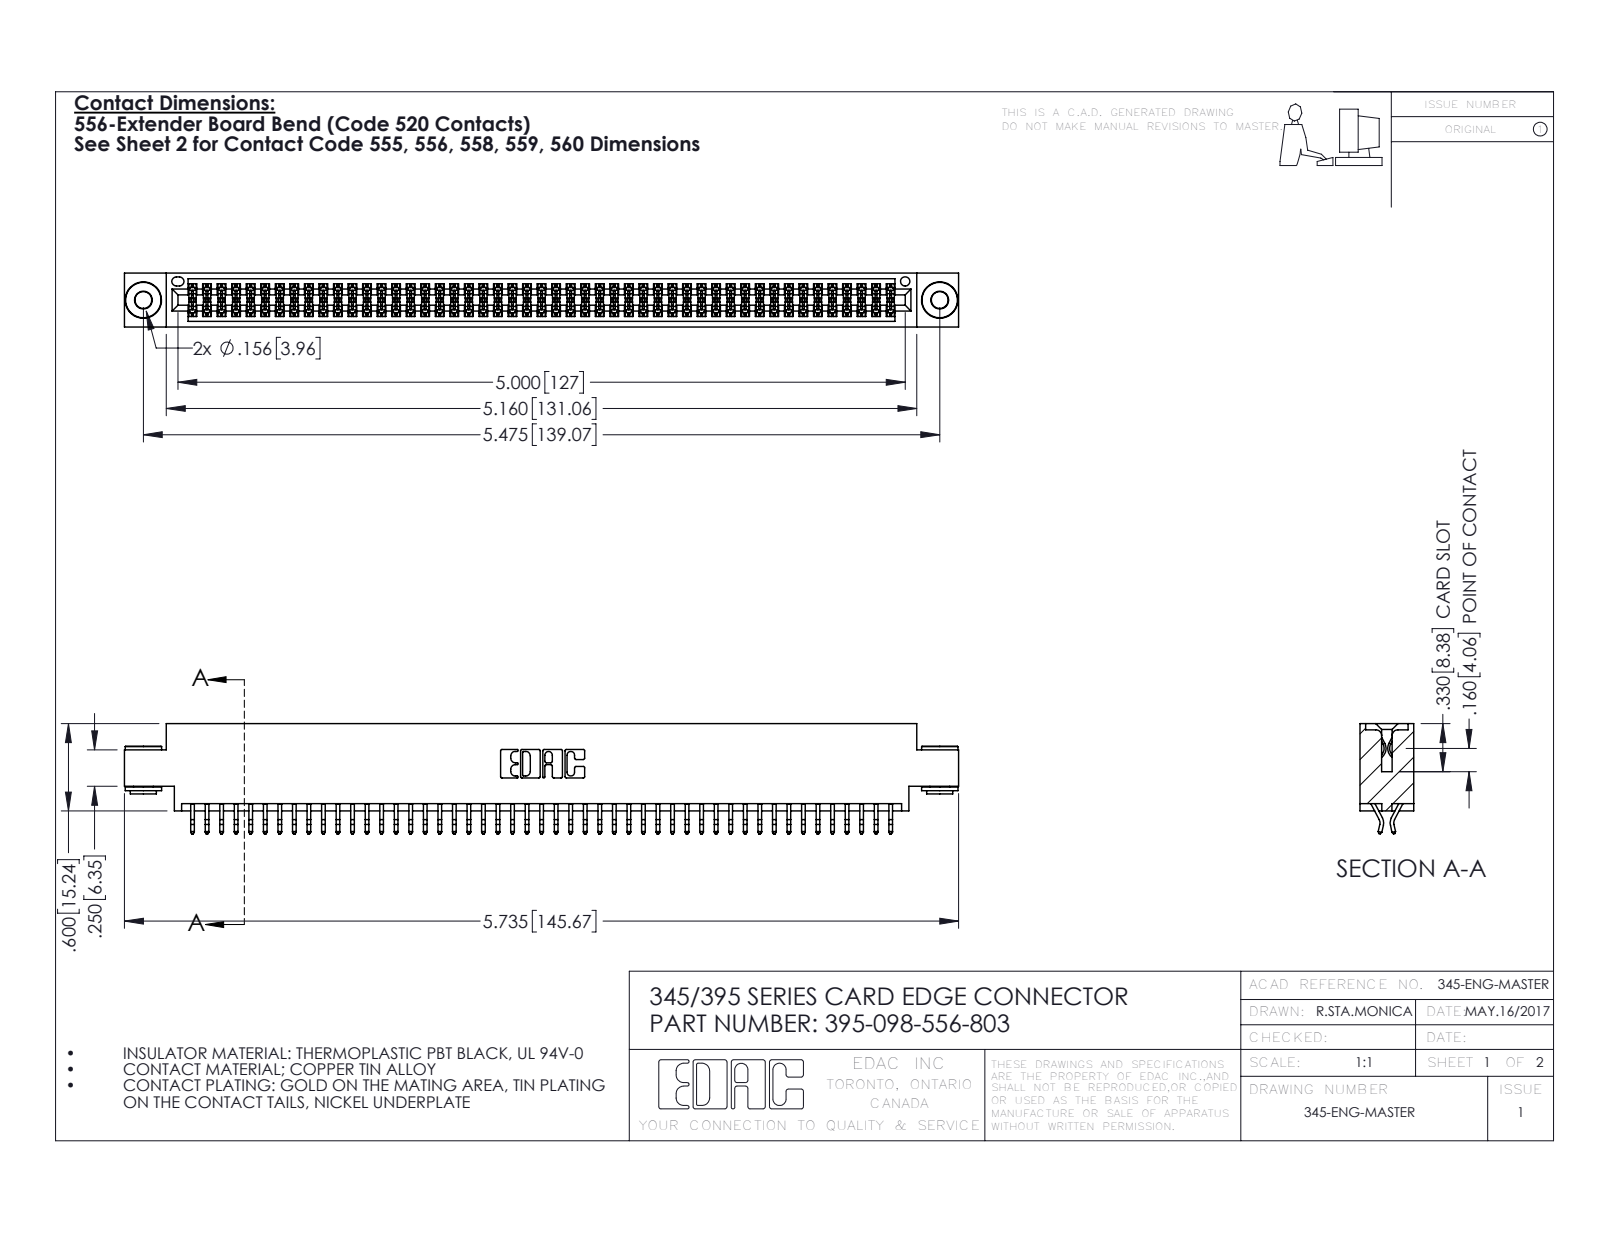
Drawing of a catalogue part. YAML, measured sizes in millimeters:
part_name: "345 Part_0.170 Offset - 0.156 Dia-TH; 395-098-556-803; 345-250-002_345-250-002-102; 345-292-001_556 Tail"
step_written_by: "SolidWorks 2016 (CONFIG_CONTROL_DESIGN)"
units: millimeters
bodies: {solids: 101, faces: 5656, planar: 3720, cylindrical: 1928, other: 8}
overall_size: [145.7, 19.2, 9.4]
volume: 14100
surface_area: 21260
round_holes:
  - {diameter: 2.9, count: 2}
  - {diameter: 4, count: 2}
  - {diameter: 1.6, count: 1}
round_bosses_or_shafts:
  - {diameter: 6.4, count: 2}
  - {diameter: 4.6, count: 2}
  - {diameter: 3.5, count: 2}
partial_cylinders:
  - {radius: 0.2, count: 147}
  - {radius: 0.3, count: 22}
  - {radius: 0.2, count: 6}
  - {radius: 0.8, count: 6}
  - {radius: 0.7, count: 3}
  - {radius: 0.3, count: 2}
  - {radius: 0.4, count: 2}
  - {radius: 0.5, count: 2}
face_to_face_distances: [1.8, 7.6, 9.4, 5.1, 0.6, 2.5, 6.9, 5.7, 4.4, 3.8]
hole_center_spacings: [6.9, 133.1, 139.1]
